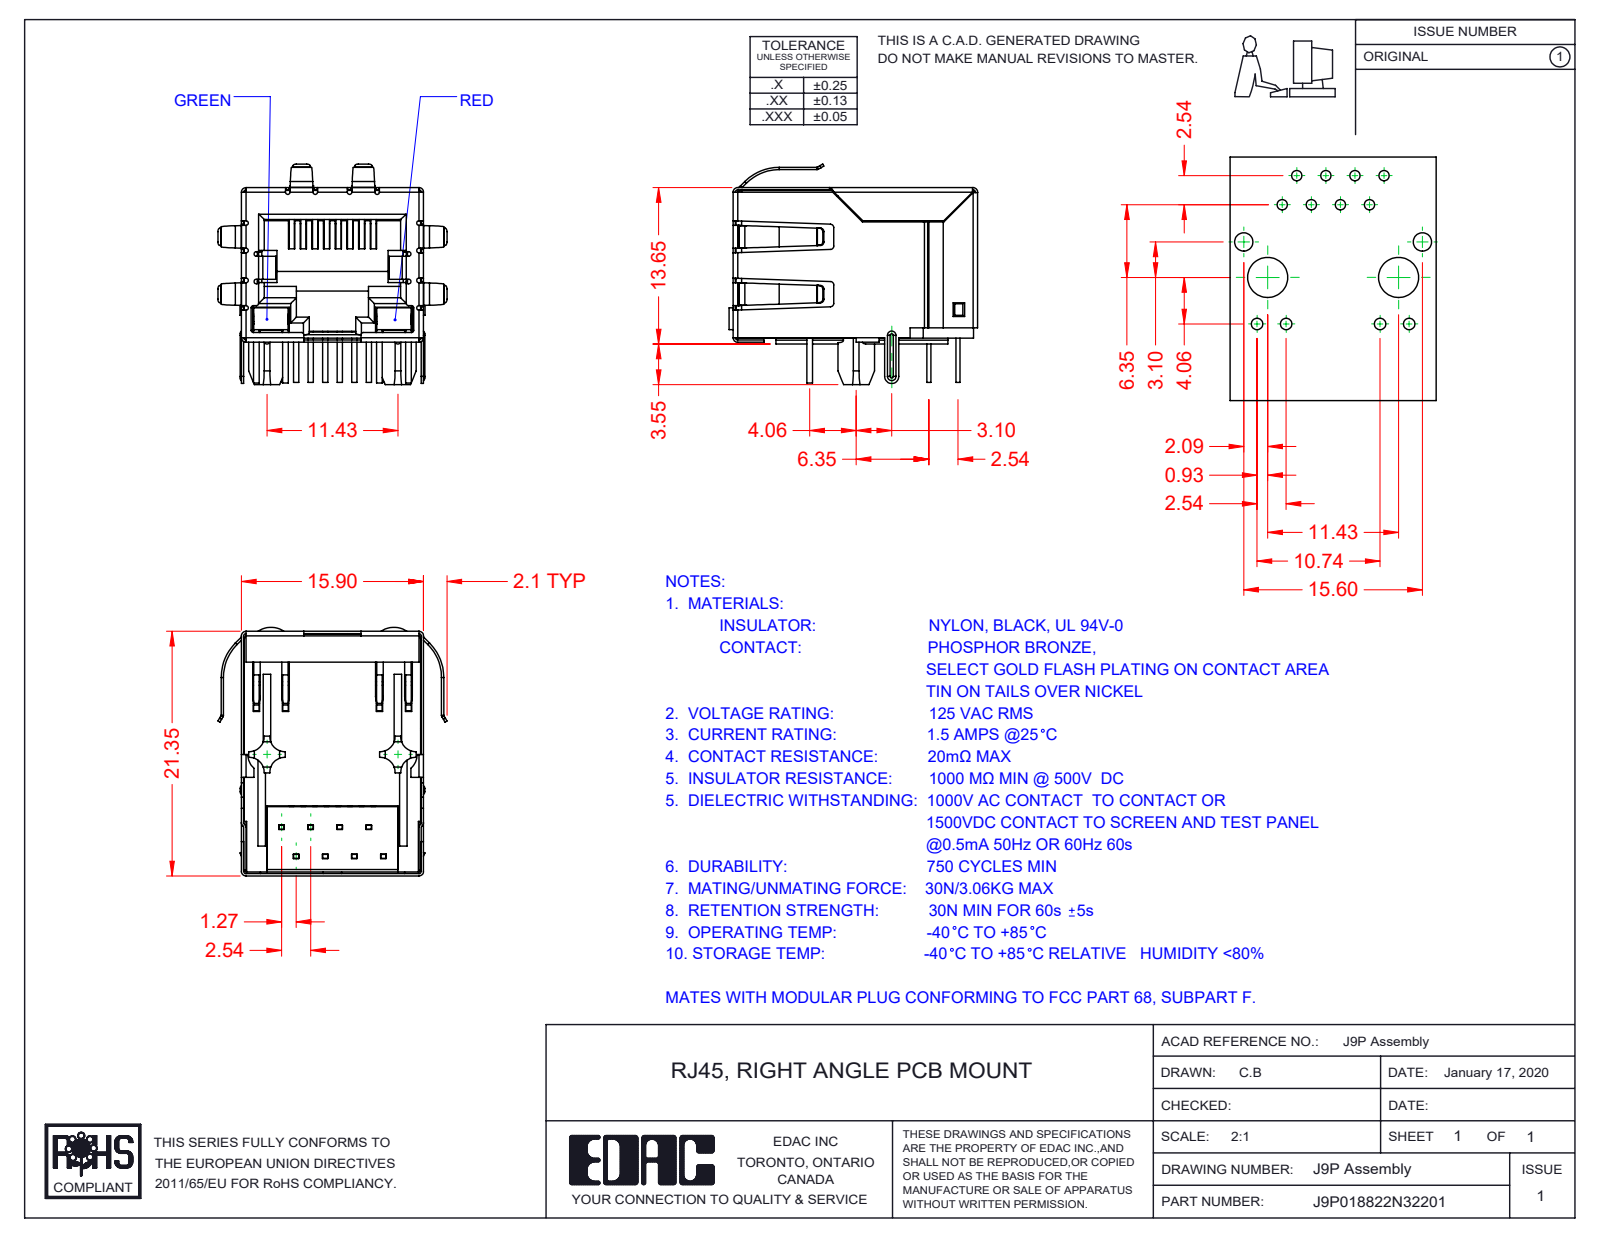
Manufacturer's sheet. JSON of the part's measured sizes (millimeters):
{"part_name": "9P-LED LED RH_2-Red; J9P018822N32202; 9P-LED Assembly; 9P-LED LED LH_3-Green (+4 more)", "step_written_by": "SolidWorks 2016 (CONFIG_CONTROL_DESIGN)", "units": "millimeters", "bodies": {"solids": 13, "faces": 1472, "planar": 1042, "cylindrical": 336, "other": 94}, "overall_size": [21.7, 20, 19.25], "volume_mm3": 2687, "surface_area_mm2": 7515, "partial_cylinders_radius": [[0.2, 39], [0.5, 22], [0.3, 20], [0.4, 16], [1.3, 8], [0.23, 5], [0.11, 4], [0.31, 4]], "face_to_face_distances": [15.45, 15.7, 15.65, 0.35, 0.54, 15.5, 12.36, 0.6, 1.4, 0.59]}
